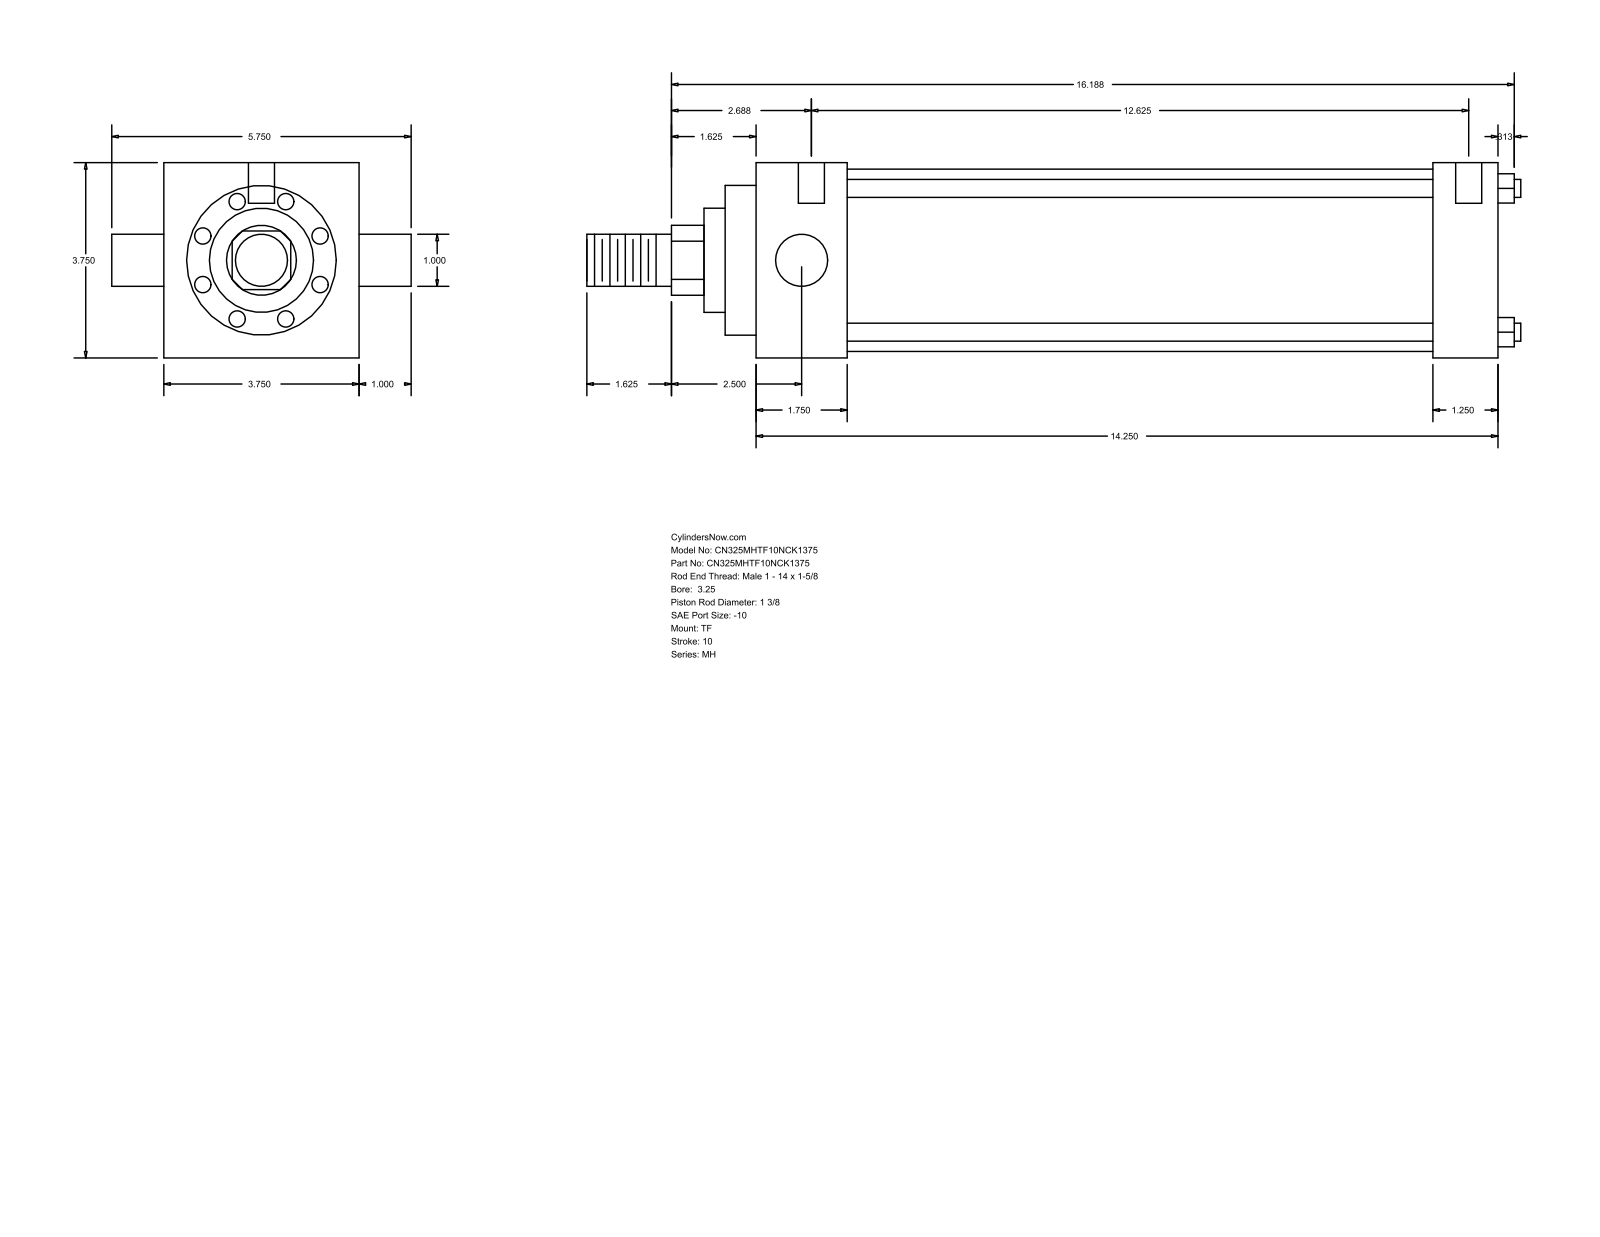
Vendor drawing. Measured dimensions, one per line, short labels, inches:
name: MH_TF__0325_1.375
written by: GSSL Pune (CONFIG_CONTROL_DESIGN)
unit: in
bodies: 0 solids, 86 faces (61 planar, 25 cylindrical, 0 other)
size: 17.937 × 5.75 × 3.75
holes: 3× ⌀0.219, 2× ⌀0.5
bosses: 4× ⌀0.345, 2× ⌀1, 1× ⌀3.5, 1× ⌀2.875, 1× ⌀2, 1× ⌀1.375
rounds: 1× R0.672
face distances: 3.75, 14.25, 1.75, 13, 11.25, 12.5, 1.25, 0.594, 2.344, 13.594
hole spacings: 0.063, 0.187, 12.625, 12.688, 12.813, 12.875
